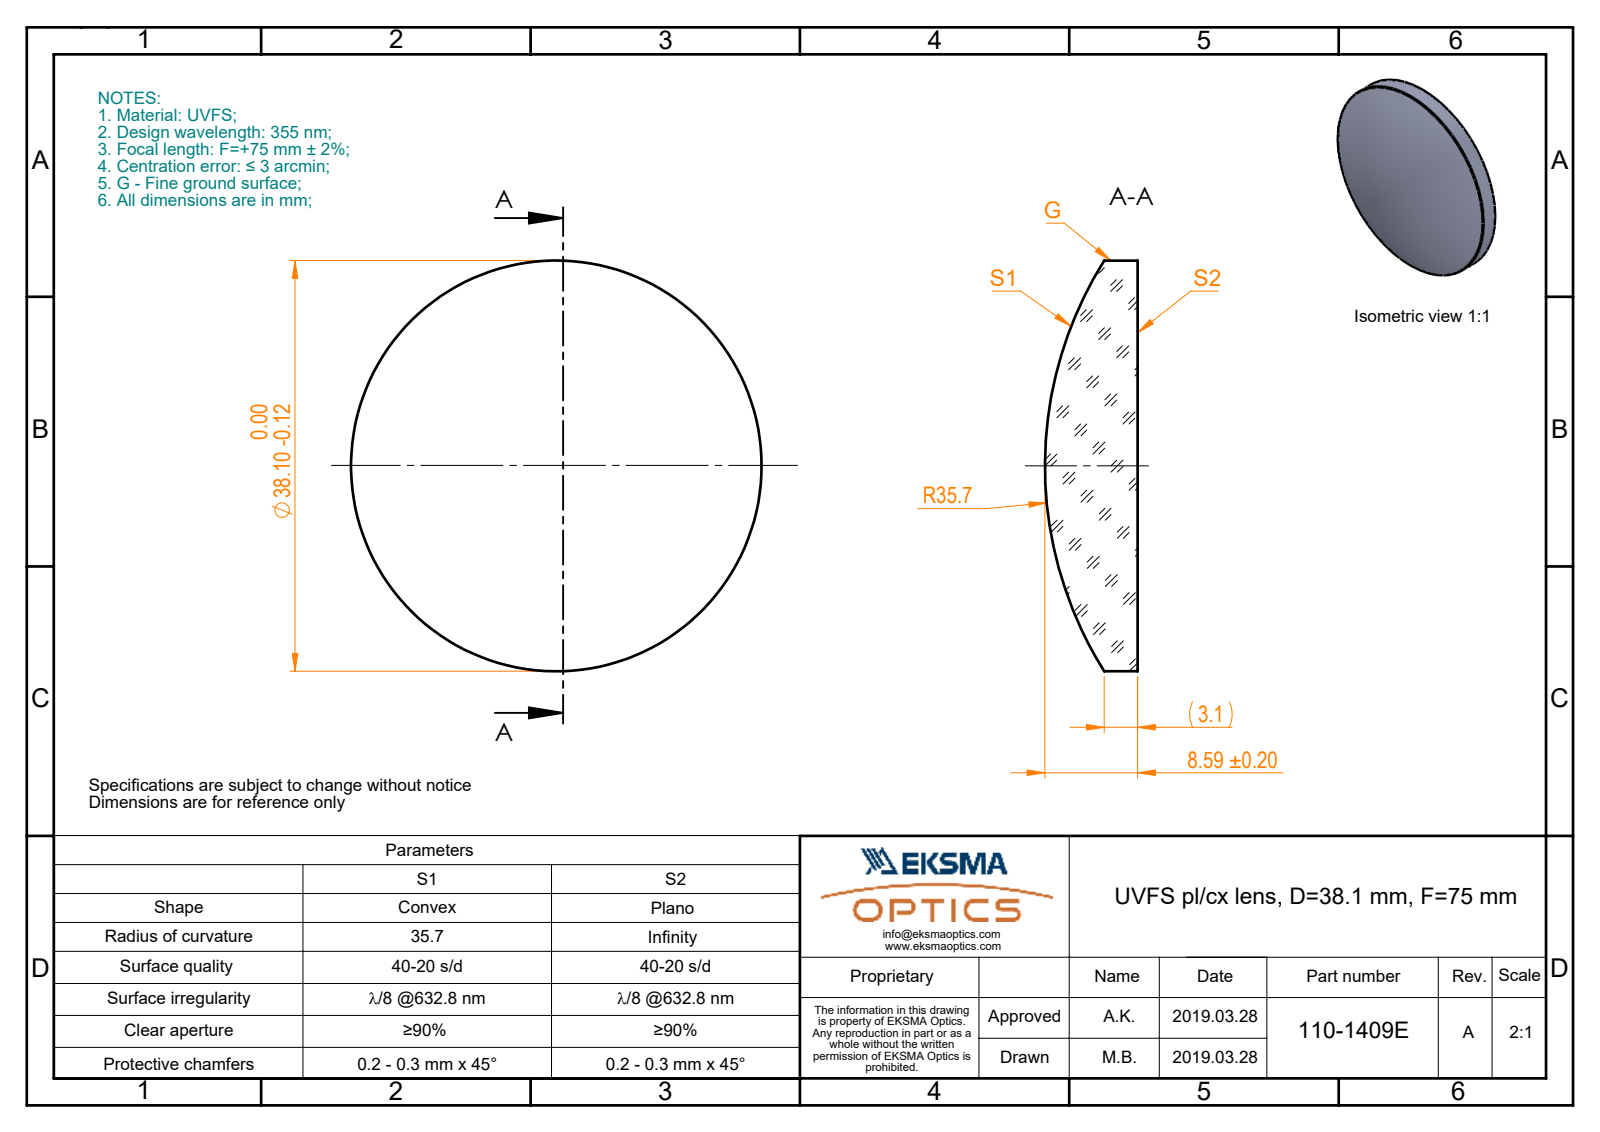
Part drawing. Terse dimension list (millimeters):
name: 110-1409E UVFS pl-cx 38.1 F75
written by: SolidWorks 2017 (CONFIG_CONTROL_DESIGN)
unit: mm
bodies: 1 solid, 5 faces (1 planar, 2 cylindrical, 2 other)
size: 38.1 × 38.1 × 8.6
volume: 6 754 mm³; area: 2 746 mm²
bosses: 1× ⌀38.1
